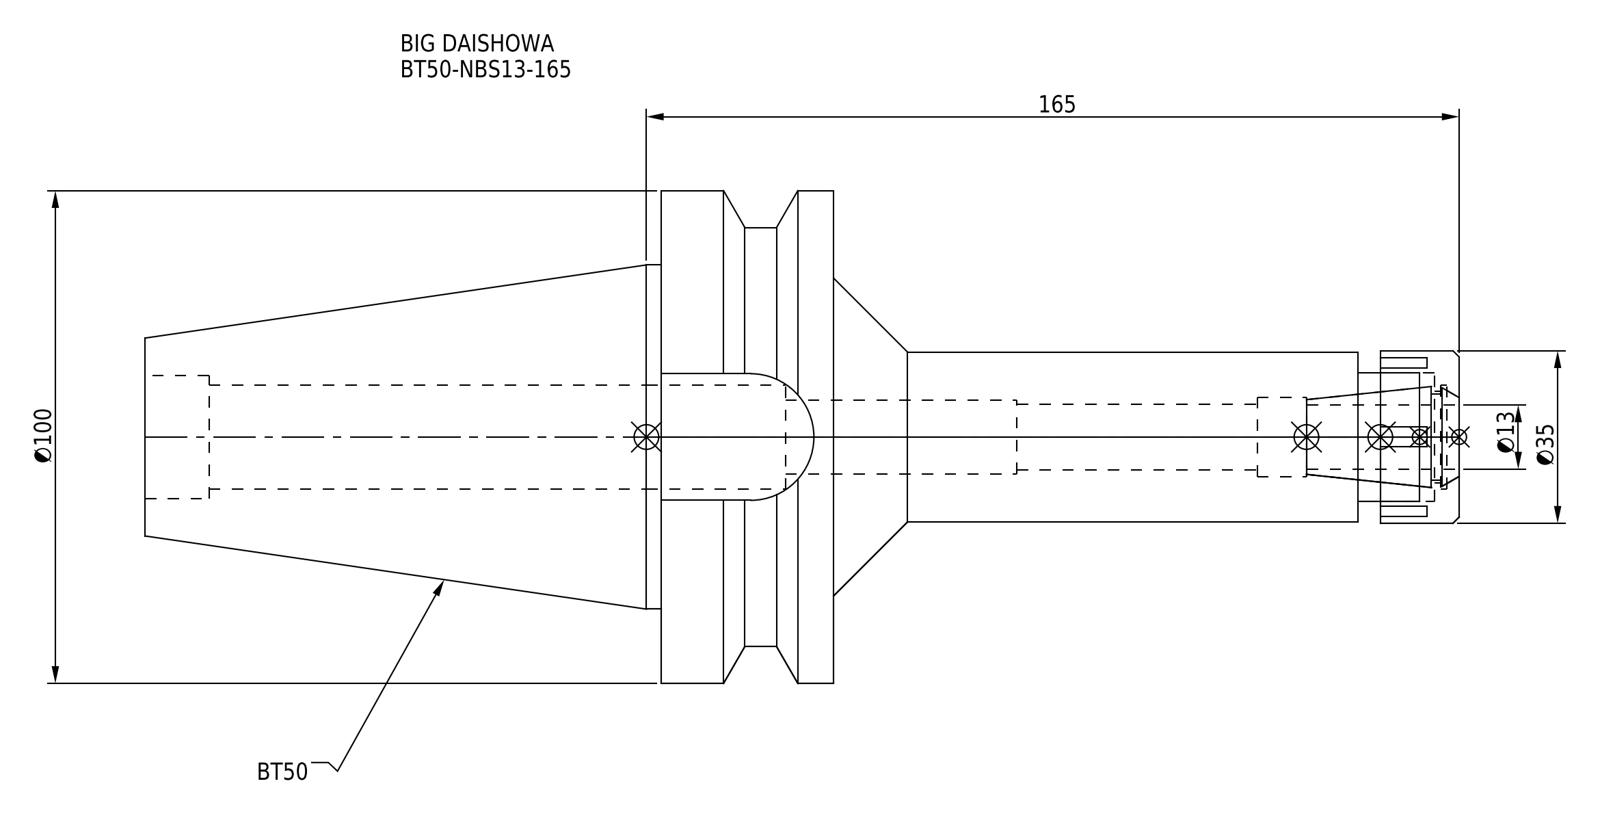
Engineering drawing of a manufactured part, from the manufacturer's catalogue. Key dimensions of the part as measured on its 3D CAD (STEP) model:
Part name (STEP PRODUCT): NBN13_1.stp; BT50-NBS13-165_1.stp; DXF_TEMP_ASSY_ASM_4_ASM.stp; BT50NB13165-130_ASM.stp (+3 more)
STEP written by: SolidWorks 2019 (CONFIG_CONTROL_DESIGN)
Units: millimetres
Bodies: 2 solids, 93 faces (45 planar, 34 cylindrical, 14 other)
Overall size (bounding box): 266.8 × 100 × 100
Volume: 553 102 mm³ · Surface area: 76 275 mm²
Round holes (diameter × count): ⌀13.3 ×1, ⌀15 ×1, ⌀16 ×1, ⌀18.5 ×1, ⌀21 ×1, ⌀21.2 ×1, ⌀25 ×1, ⌀26 ×1
Round bosses / shafts (diameter × count): ⌀100 ×1, ⌀85 ×1, ⌀69.85 ×1, ⌀35 ×1, ⌀34.5 ×1
Partial cylindrical surfaces — rounded edges, fillets, slot ends (radius × count): R12.85 ×1
Main face-to-face distances: 35, 139.8, 104.8, 70.8, 127, 162, 266.8, 20.5, 8, 25.7
